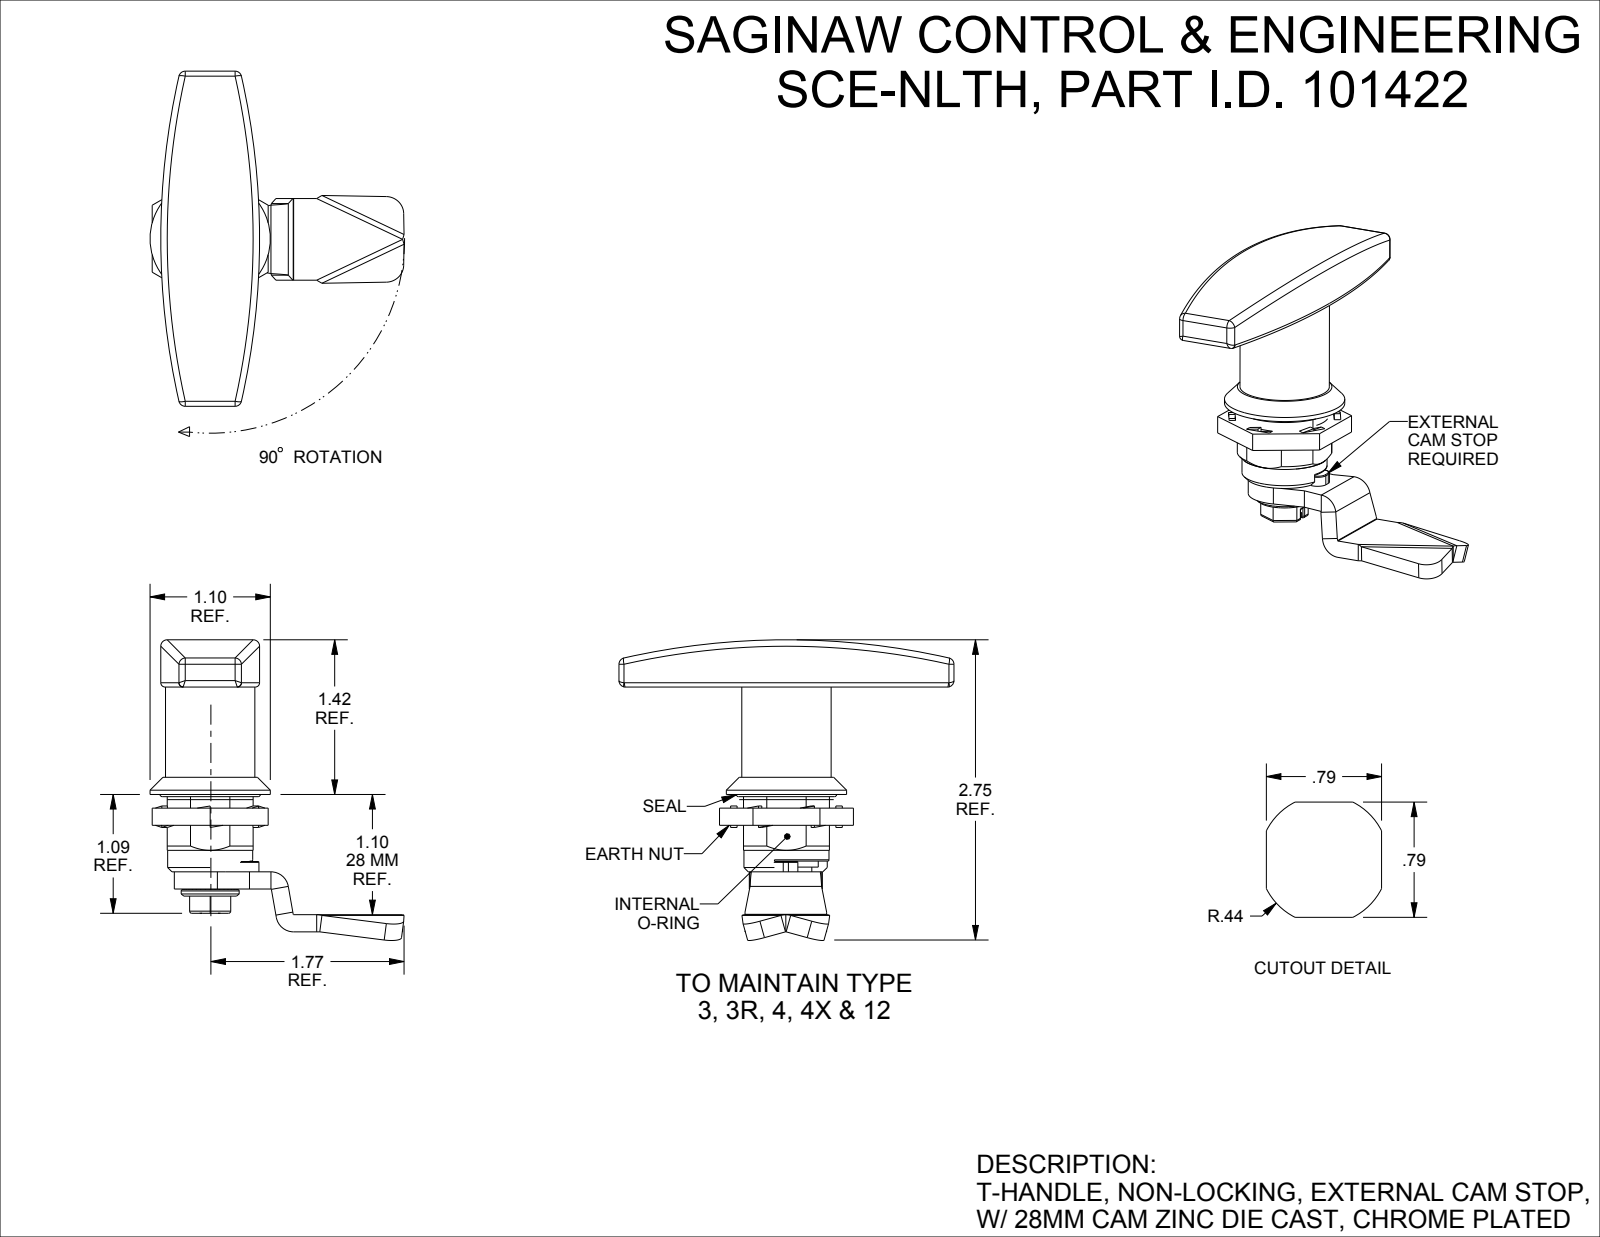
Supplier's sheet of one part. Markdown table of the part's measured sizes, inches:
| quantity | value |
| --- | --- |
| part name | SCE-NLTH |
| STEP written by | SolidWorks 2021 (AUTOMOTIVE_DESIGN) |
| units | inches |
| bodies | 6 solids, 355 faces (156 planar, 122 cylindrical, 77 other) |
| overall size | 3.071 × 2.755 × 2.328 |
| volume | 1.802 in³ |
| surface area | 26.51 in² |
| round holes (diameter × count) | 0.201 × 2, 0.102 × 1, 0.315 × 1, 0.394 × 1, 0.634 × 1, 0.799 × 1 |
| round bosses / shafts (diameter × count) | 1.102 × 1, 0.819 × 1, 0.78 × 1, 0.583 × 1, 0.531 × 1, 0.465 × 1, 0.217 × 1 |
| partial cylindrical surfaces (radius × count) | 0.012 × 30, 0.02 × 16, 0.059 × 8, 0.157 × 4, 6.742 × 3, 0.004 × 2, 0.008 × 2, 0.087 × 2 |
| main face-to-face distances | 0.157, 1.259, 0.866, 0.976, 0.282, 0.393, 0.584, 0.709, 1.101, 0.55 |
| hole center spacings | 0.433 |
